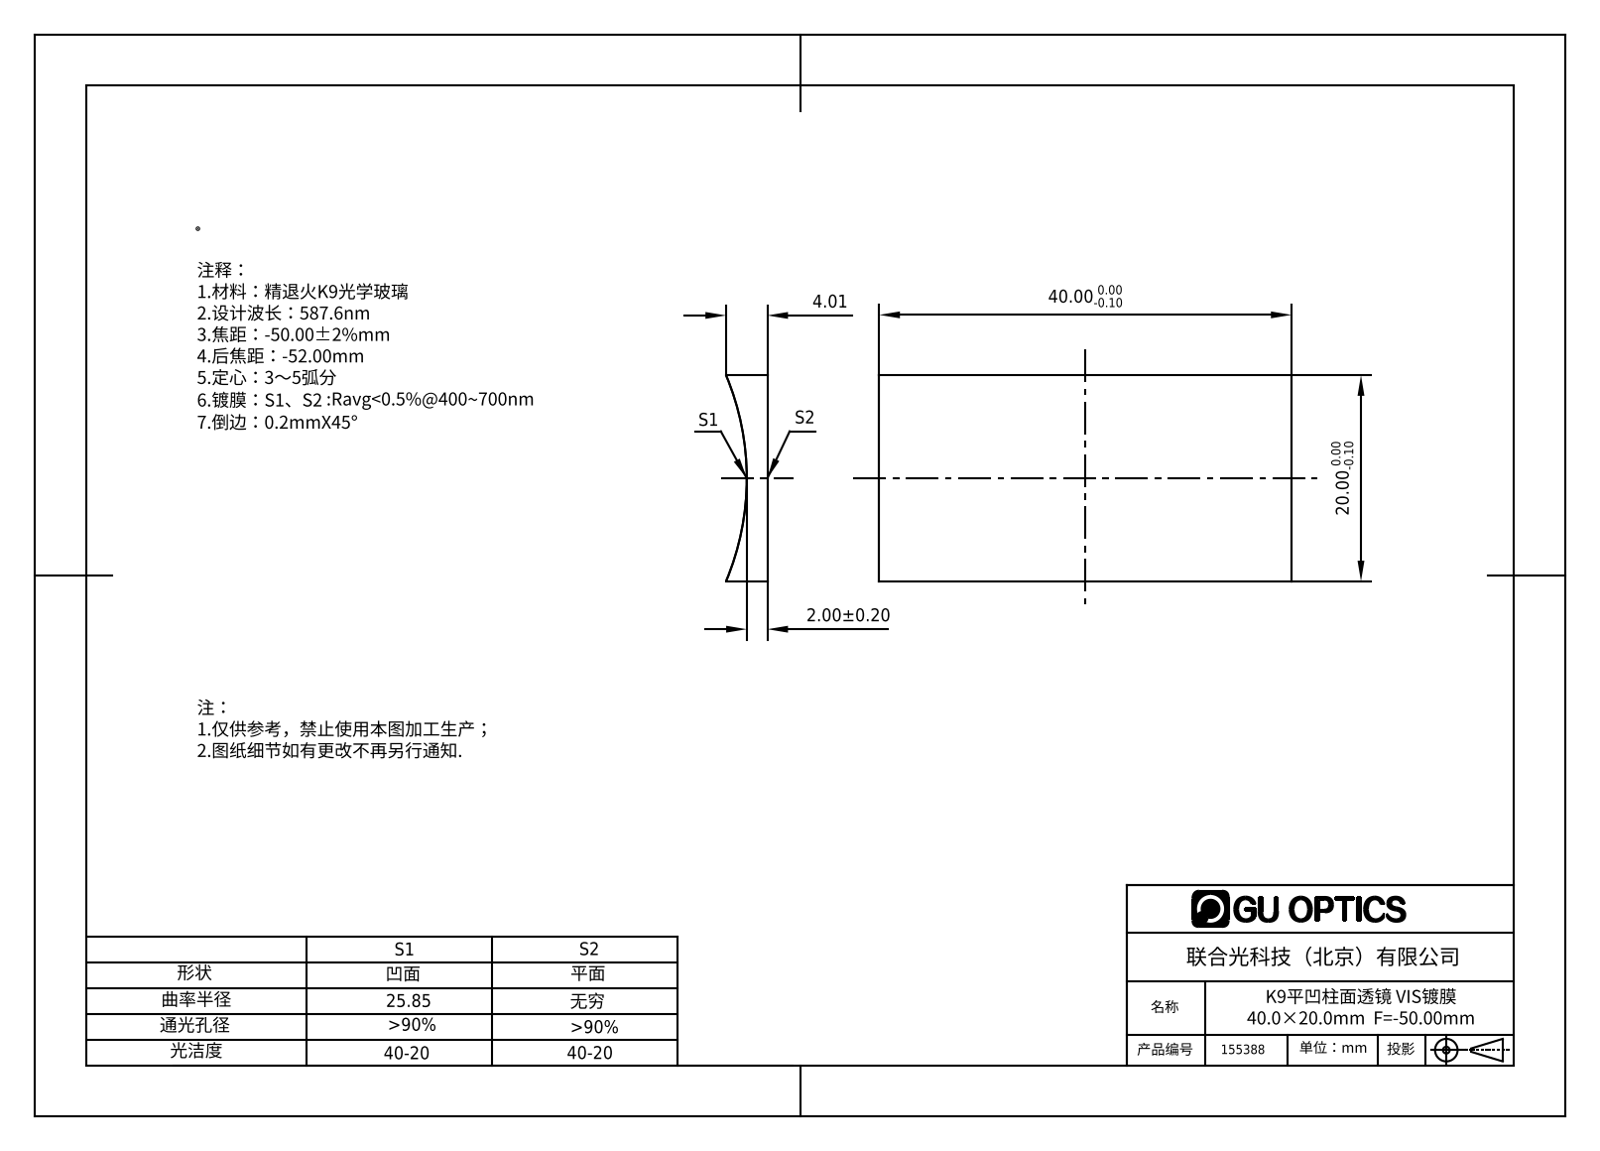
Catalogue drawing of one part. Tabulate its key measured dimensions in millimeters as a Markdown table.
| quantity | value |
| --- | --- |
| part name | 155355 |
| STEP written by | SolidWorks 2016 (AUTOMOTIVE_DESIGN) |
| units | millimeters |
| bodies | 1 solid, 6 faces (5 planar, 1 cylindrical, 0 other) |
| overall size | 40 × 20 × 4.01 |
| volume | 2 128 mm³ |
| surface area | 2 049 mm² |
| partial cylindrical surfaces (radius × count) | 25.85 × 1 |
| main face-to-face distances | 20, 40 |
